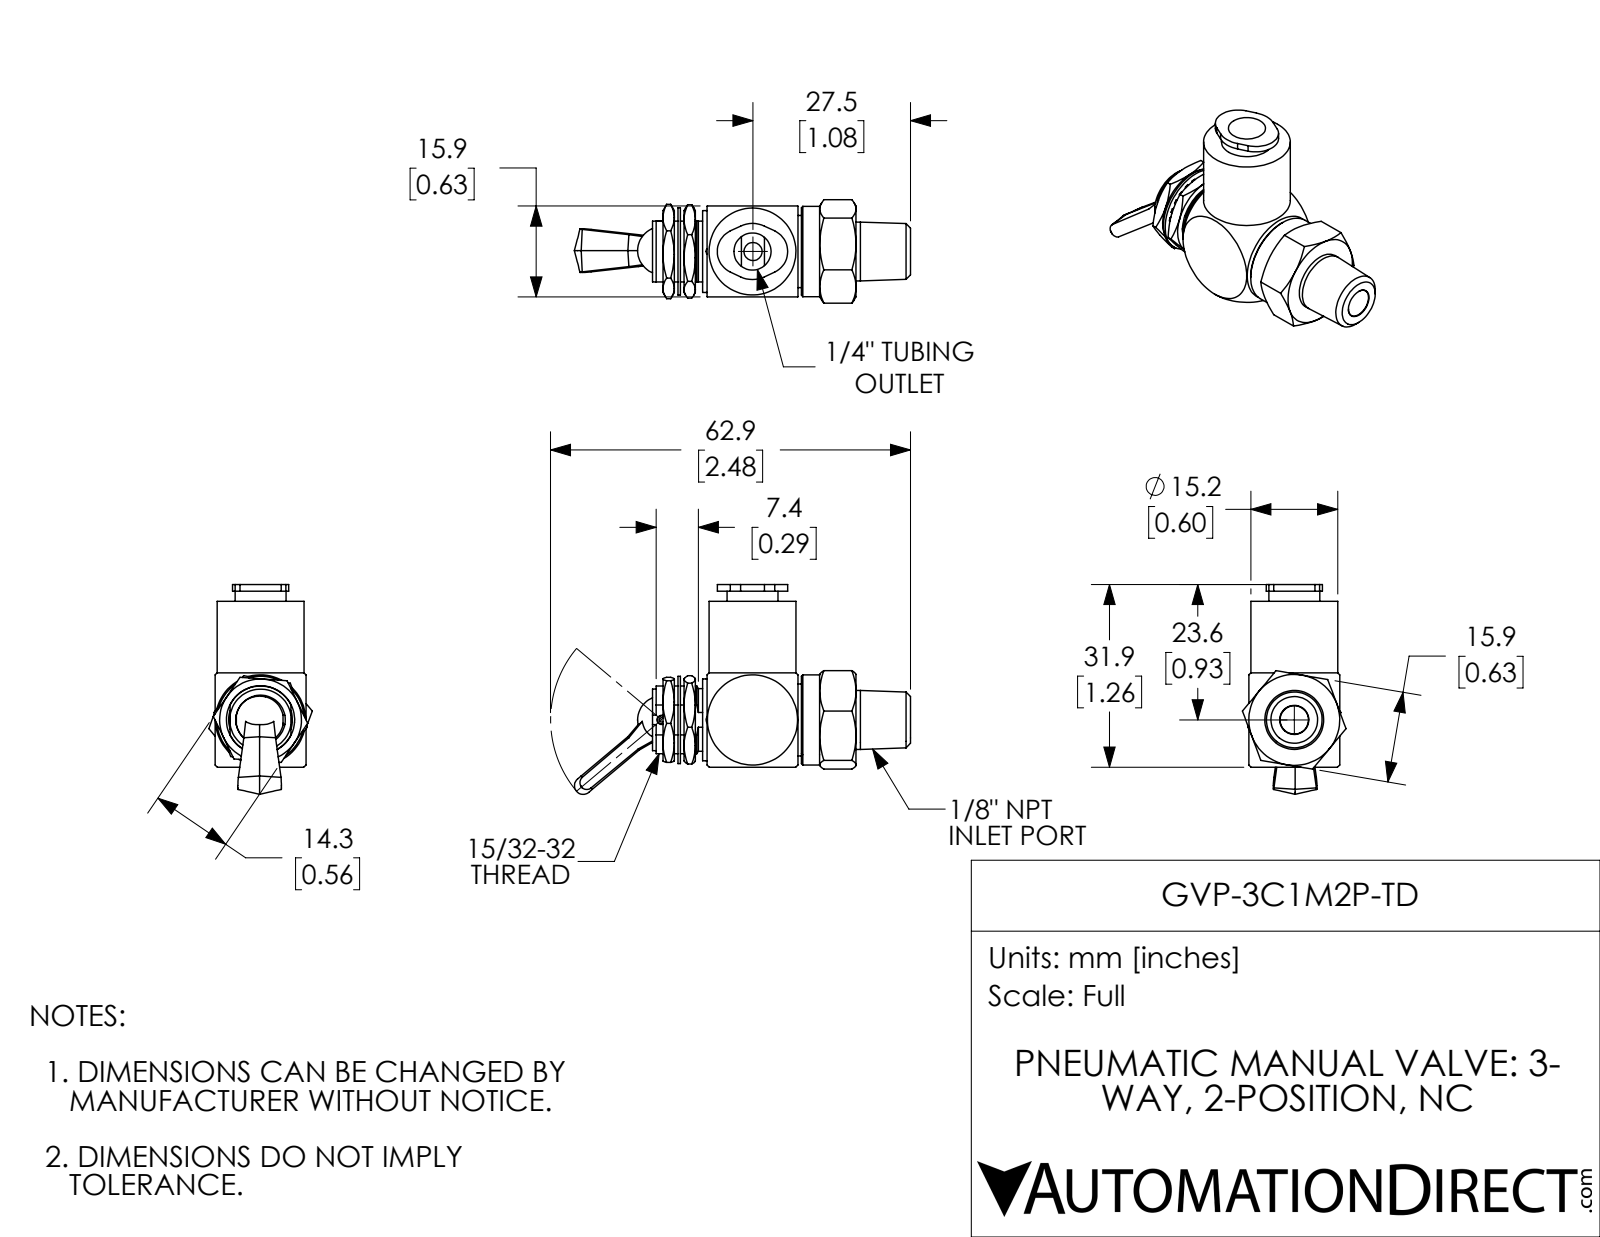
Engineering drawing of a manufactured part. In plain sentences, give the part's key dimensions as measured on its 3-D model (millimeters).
The part is named "GVP-3C1M2P-TD". Its 3-D file was written by "SolidWorks 2018 (AUTOMOTIVE_DESIGN)". It is 8 solids with 331 faces: 124 planar, 137 cylindrical and 70 other. Overall it measures 58.7 by 36.6 by 18.1 millimeters. Its volume is 8 130 cubic millimeters and its surface area 8 419 square millimeters. Round holes: 3 of diameter 1.6, 2 of diameter 3.2, 1 of diameter 0.8, 1 of diameter 1.8, 1 of diameter 5, 1 of diameter 6.3, 1 of diameter 6.5, 1 of diameter 8.6, 1 of diameter 9.6, 1 of diameter 11.1, 1 of diameter 11.9, 1 of diameter 12.7. Round bosses or shafts: 1 of diameter 15.7, 1 of diameter 15.2, 1 of diameter 15.2, 1 of diameter 14.3, 1 of diameter 12.6, 1 of diameter 11.3, 1 of diameter 10.9, 1 of diameter 10.7. Partial cylindrical surfaces (rounded edges, fillets, slot ends): 2 of radius 4, 1 of radius 4.9, 1 of radius 5.9, 1 of radius 6.1, 1 of radius 6.6. The main face-to-face distances are 15.9, 1.8, 29, 2.4, 8.4, 7.7, 3.3, 6.8, 0.6, 1.1. The hole center spacings are 7.4, 7.3, 8.6, 16.
